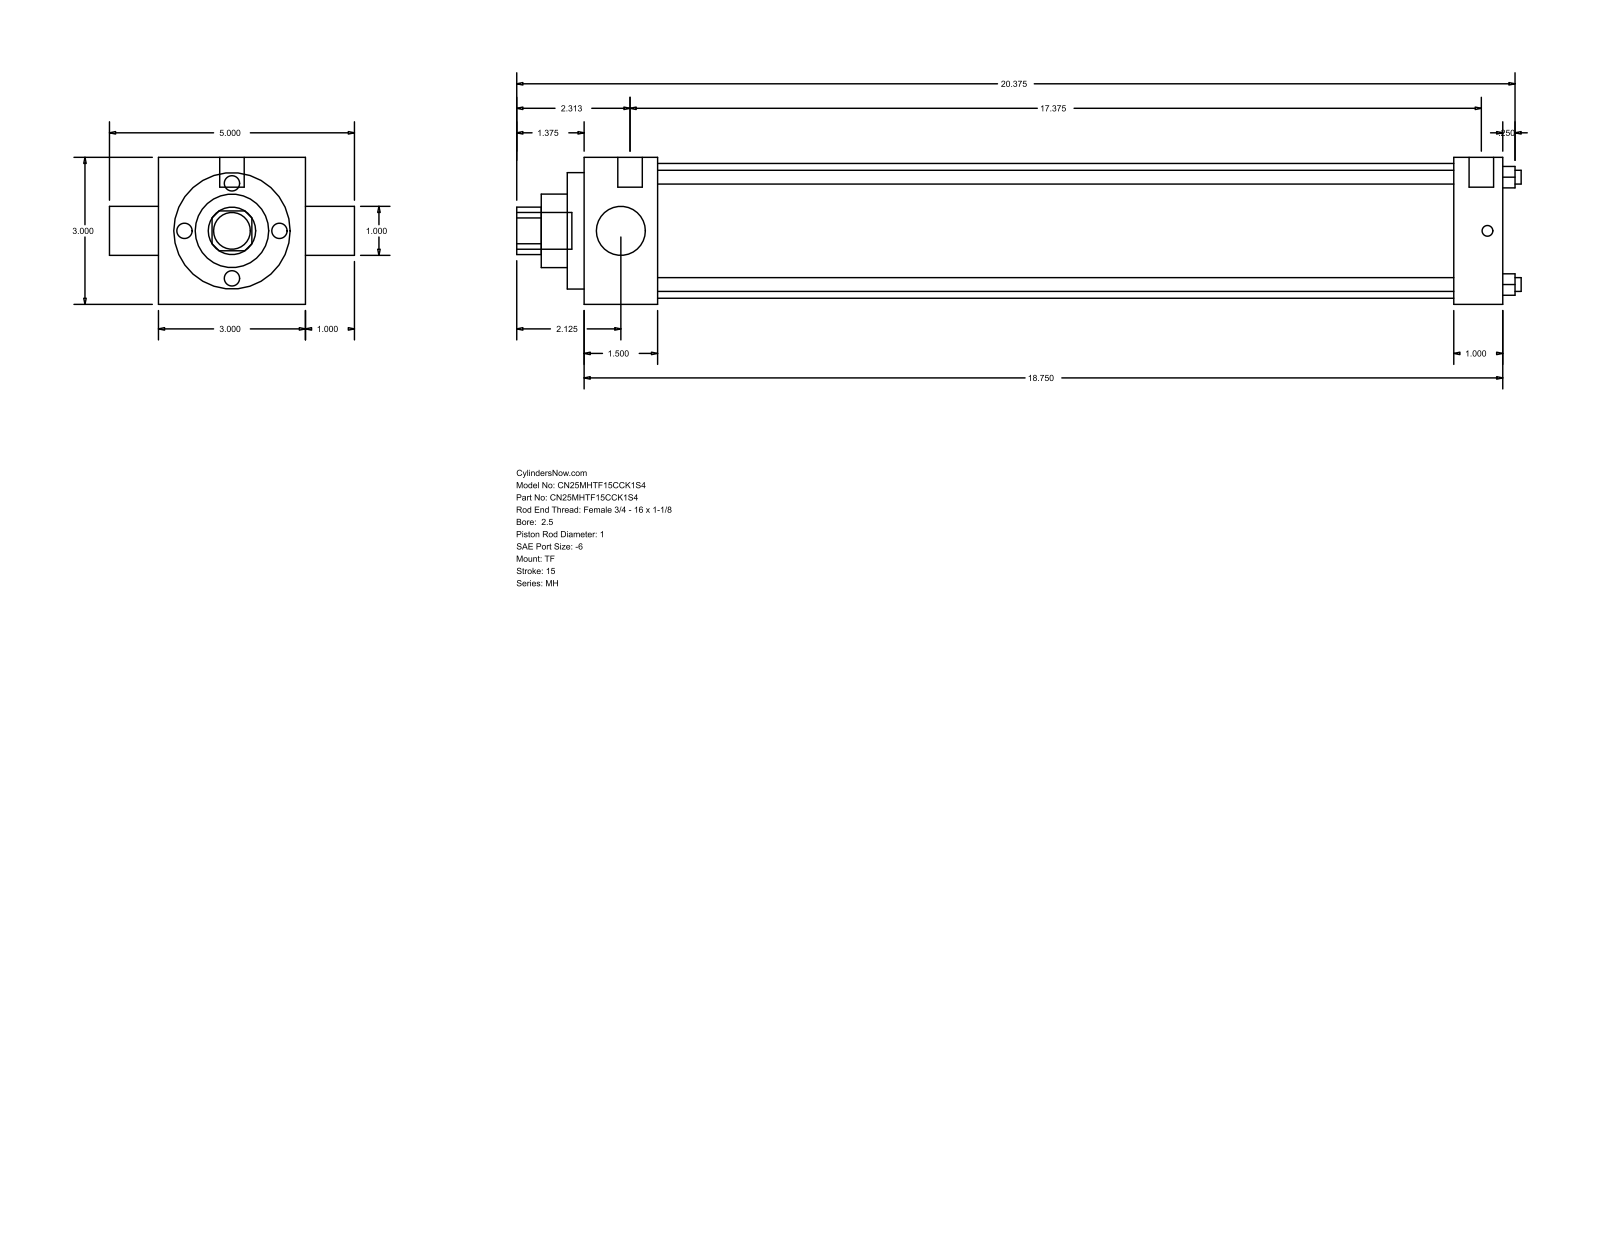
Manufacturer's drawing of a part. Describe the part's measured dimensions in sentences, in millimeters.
The part is named "MH_TF__0250_1". Its 3-D file was written by "GSSL Pune (CONFIG_CONTROL_DESIGN)". It is 0 solids with 86 faces: 61 planar, 25 cylindrical and 0 other. Overall it measures 520.7 by 127 by 76.2 millimeters. Round holes: 4 of diameter 7.14, 2 of diameter 25.4, 1 of diameter 38.1, 1 of diameter 60.33, 1 of diameter 69.85. Round bosses or shafts: 3 of diameter 5.56, 2 of diameter 12.7, 1 of diameter 19.05. Partial cylindrical surfaces (rounded edges, fillets, slot ends): 1 of radius 12.29. The main face-to-face distances are 76.2, 476.26, 38.11, 438.15, 450.85, 412.74, 25.41, 8.73, 46.84, 459.58. The hole center spacings are 39.33, 55.62, 78.66.
